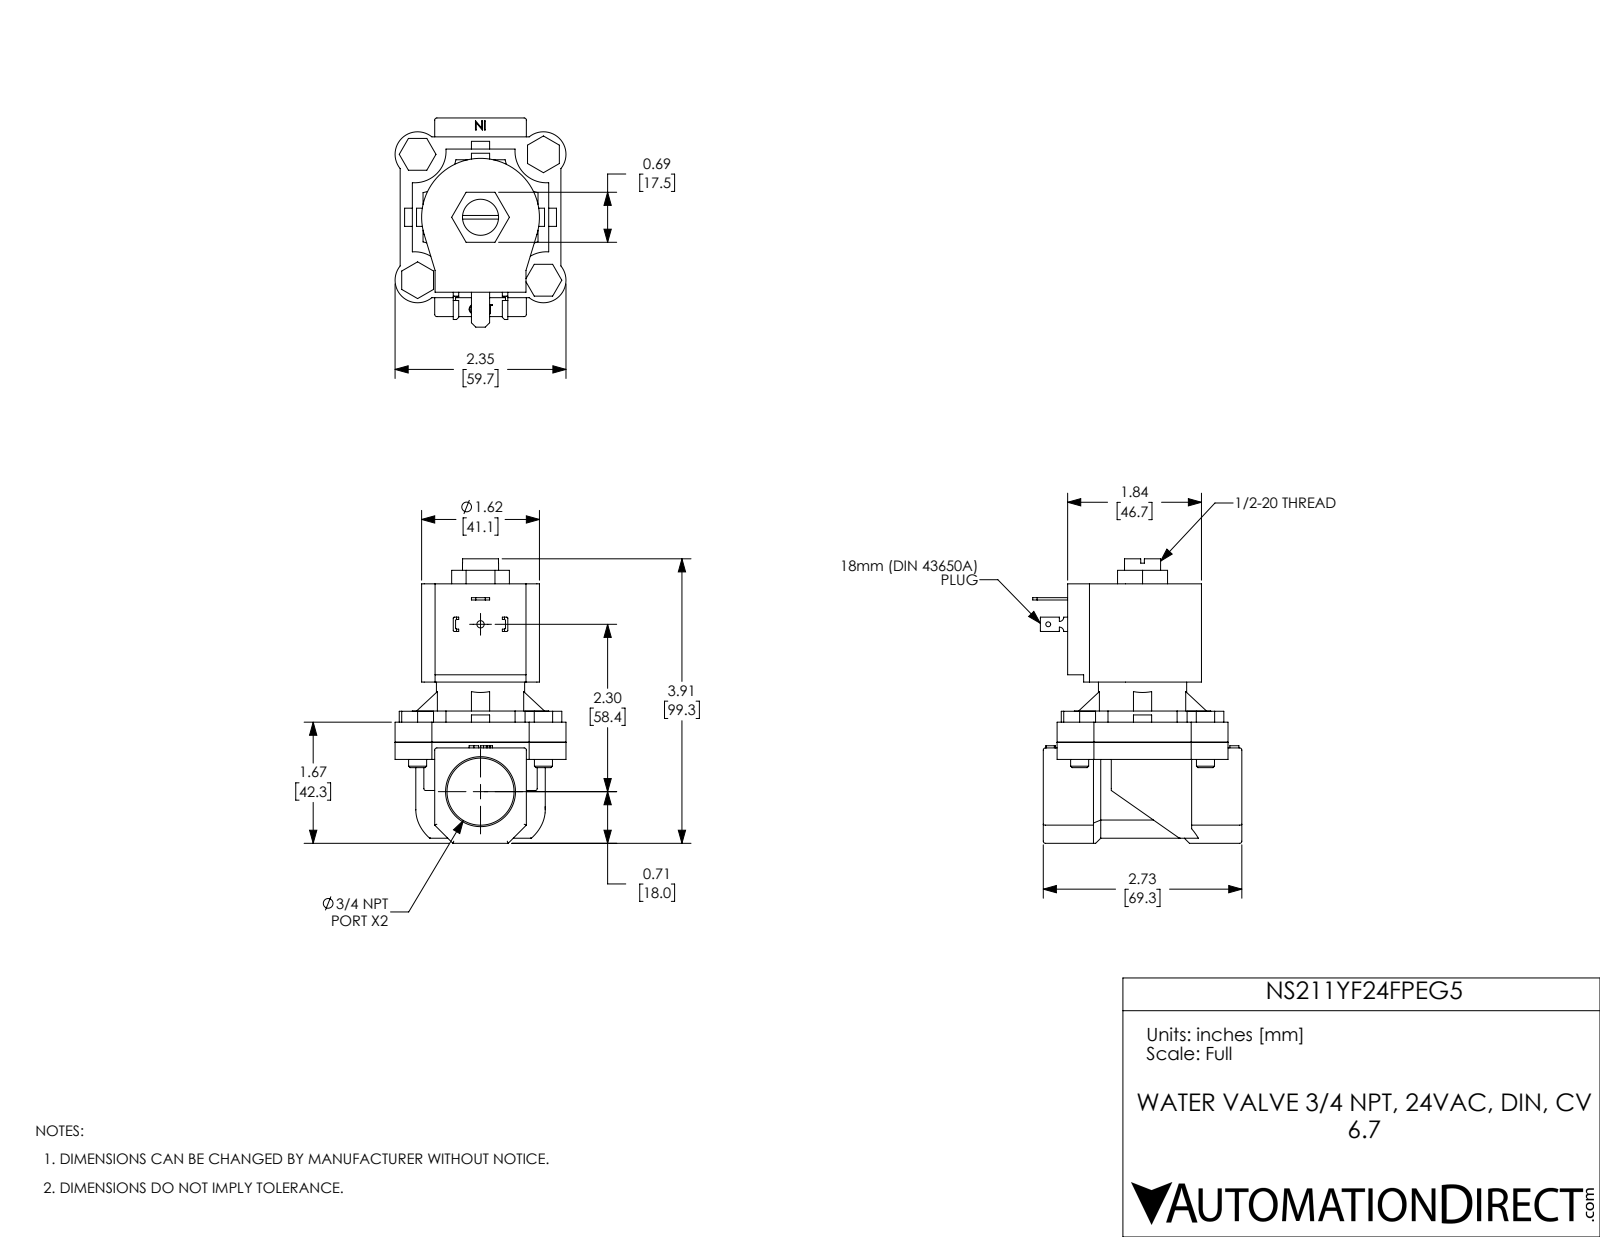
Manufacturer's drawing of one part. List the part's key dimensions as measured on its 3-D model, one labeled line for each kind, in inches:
Part name (STEP PRODUCT): NS211YF24FPEG5
STEP written by: SolidWorks 2017 (AUTOMOTIVE_DESIGN)
Units: inches
Bodies: 11 solids, 387 faces (241 planar, 113 cylindrical, 33 other)
Overall size (bounding box): 3.91 × 2.875 × 2.35
Volume: 9.997 in³ · Surface area: 68.35 in²
Round holes (diameter × count): ⌀0.25 ×4, ⌀0.067 ×1, ⌀0.1 ×1, ⌀0.496 ×1, ⌀0.512 ×1, ⌀0.922 ×1, ⌀1.155 ×1
Round bosses / shafts (diameter × count): ⌀0.248 ×4, ⌀1.213 ×1
Partial cylindrical surfaces — rounded edges, fillets, slot ends (radius × count): R0.03 ×15, R0.015 ×8, R0.31 ×4, R0.432 ×4, R0.579 ×4, R0.06 ×2, R0.81 ×1, R0.89 ×1
Main face-to-face distances: 0.276, 2.177, 1.901, 0.236, 0.512, 2.413, 1.063, 0.827, 0.551, 1.35
Hole centre spacings: 1.223, 1.73, 2.446, 2.3
